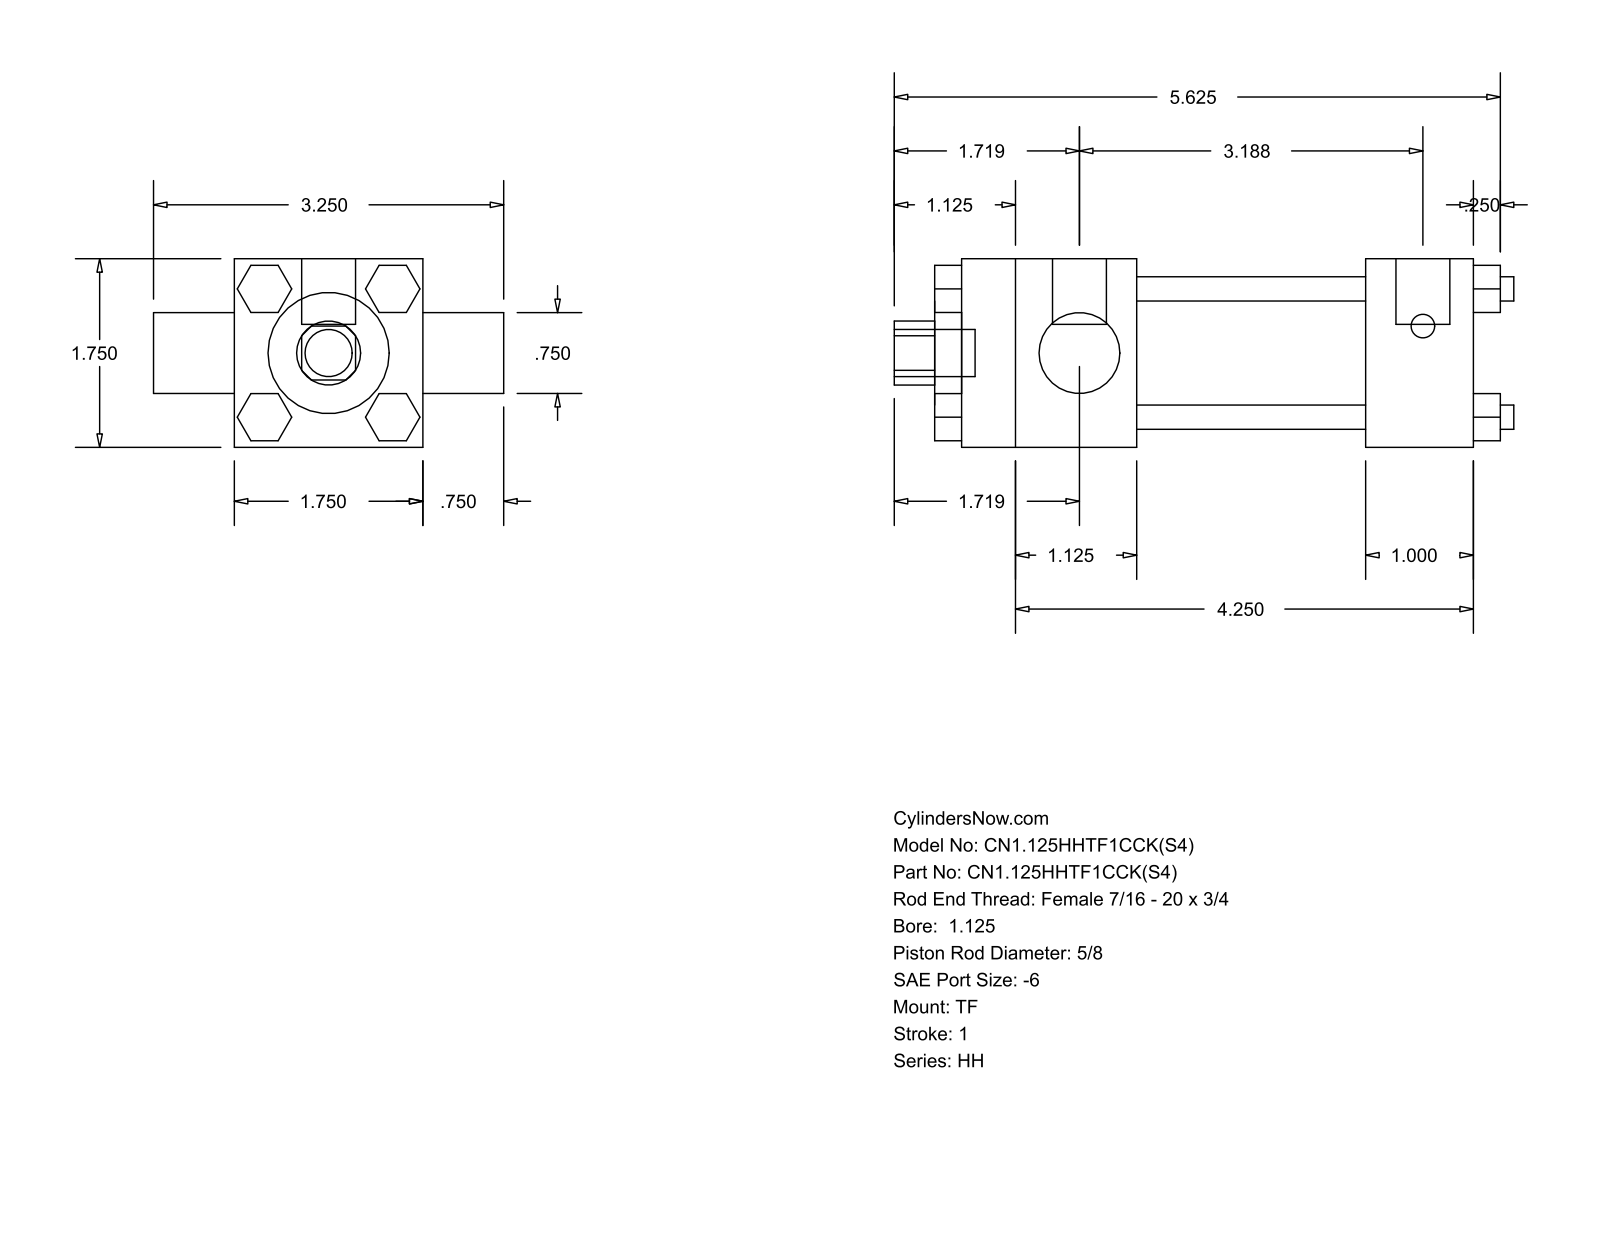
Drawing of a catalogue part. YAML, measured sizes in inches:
part_name: "HH_TF__0112_0.625"
step_written_by: "GSSL Pune (CONFIG_CONTROL_DESIGN)"
units: inches
bodies: {solids: 0, faces: 120, planar: 92, cylindrical: 28, other: 0}
overall_size: [5.75, 3.25, 1.75]
round_holes:
  - {diameter: 0.625, count: 1}
  - {diameter: 0.75, count: 1}
  - {diameter: 1.125, count: 1}
  - {diameter: 1.375, count: 1}
round_bosses_or_shafts:
  - {diameter: 0.225, count: 4}
  - {diameter: 0.219, count: 3}
  - {diameter: 0.5, count: 2}
  - {diameter: 0.437, count: 1}
partial_cylinders:
  - {radius: 0.297, count: 1}
face_to_face_distances: [1.75, 5, 0.25, 0.437, 2.125, 3.125, 1, 1.625, 3.75, 4.75]
